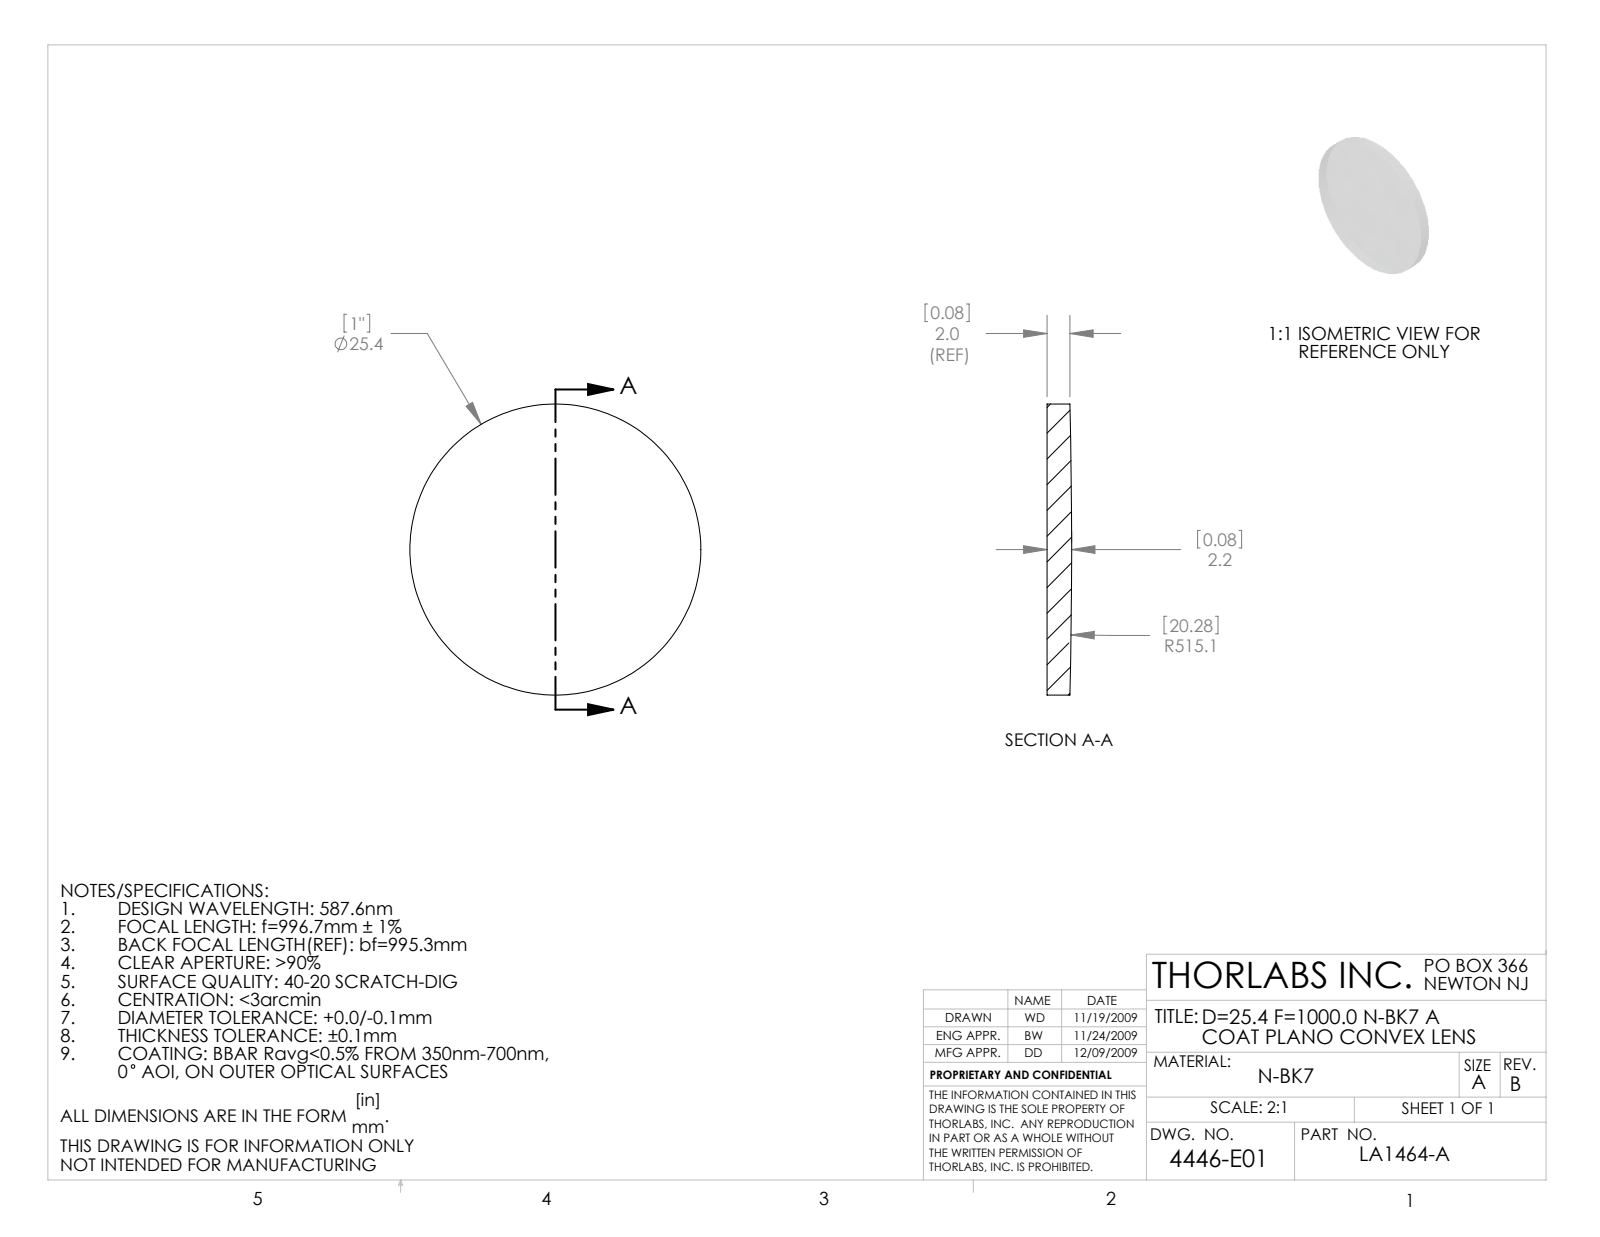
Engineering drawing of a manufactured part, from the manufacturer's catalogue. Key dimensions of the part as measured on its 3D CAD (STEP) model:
Part name (STEP PRODUCT): 4446-E0W
STEP written by: SolidWorks 2009 (AUTOMOTIVE_DESIGN)
Units: millimetres
Bodies: 1 solid, 5 faces (1 planar, 2 cylindrical, 2 other)
Overall size (bounding box): 25.4 × 25.4 × 2.15
Volume: 1 050 mm³ · Surface area: 1 173 mm²
Round bosses / shafts (diameter × count): ⌀25.4 ×1
